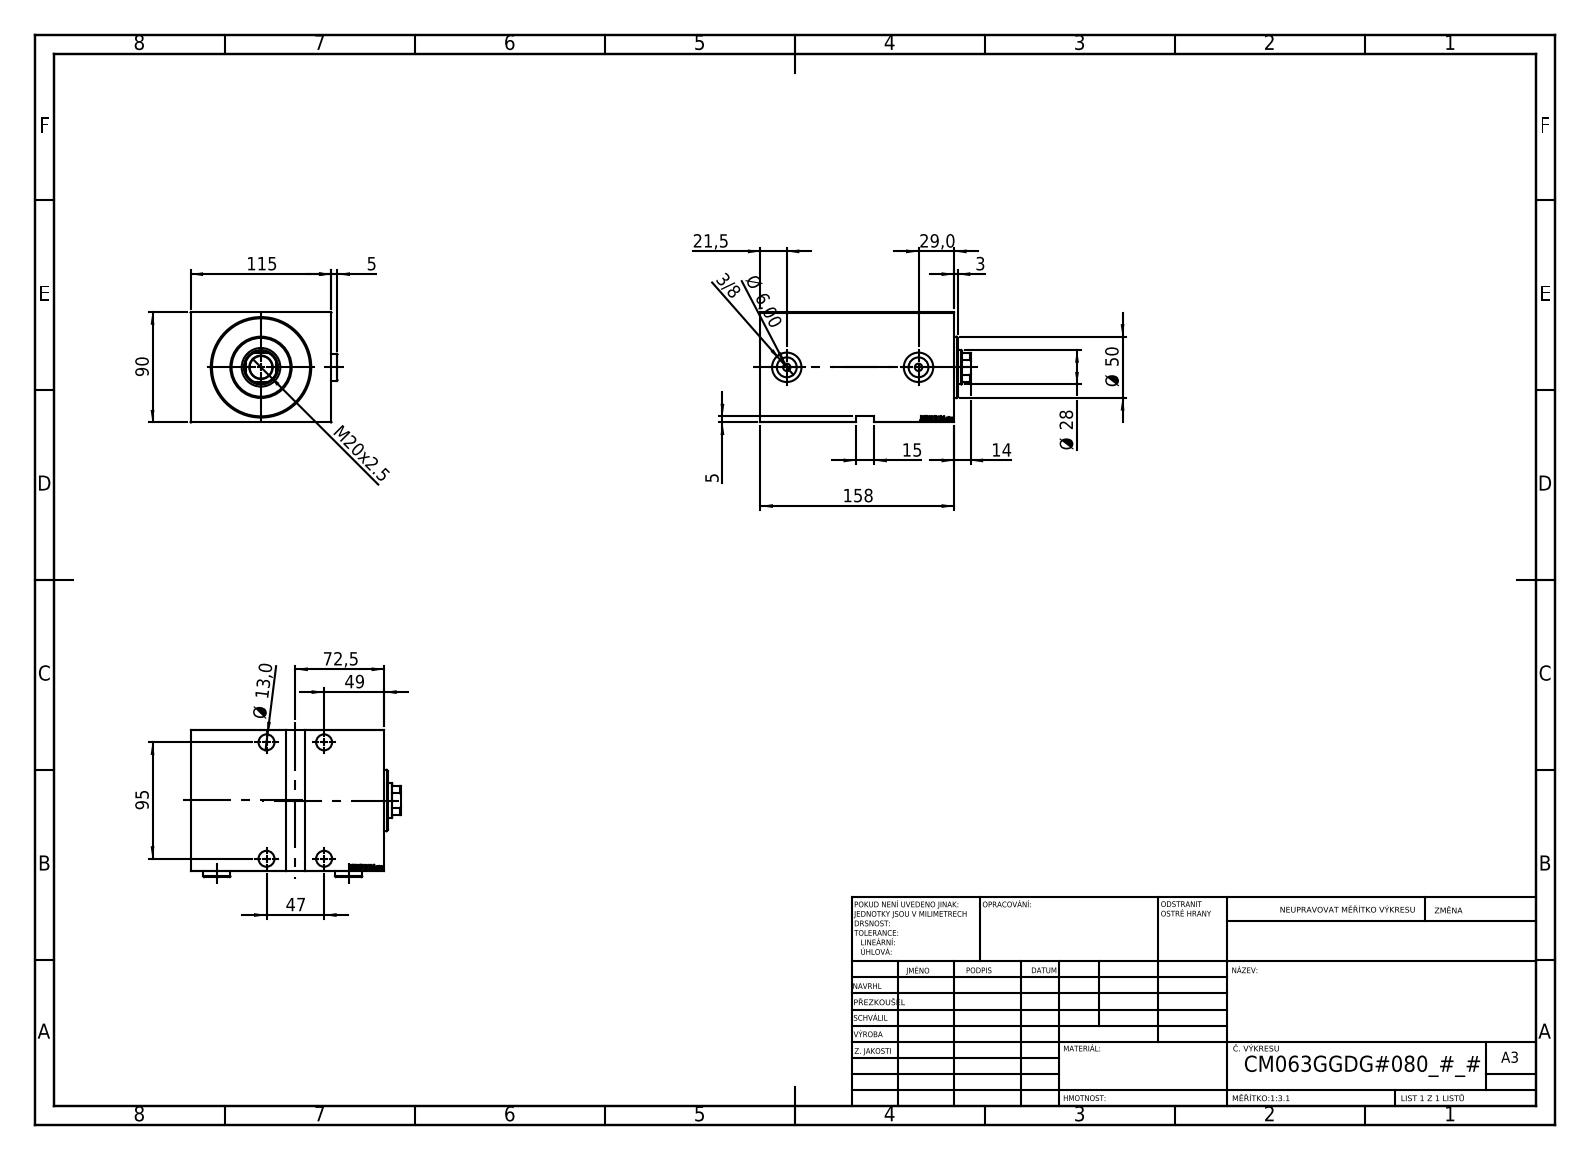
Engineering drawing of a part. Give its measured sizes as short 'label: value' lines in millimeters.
name: V450CM_VC_G; V450CM_G_VCP; Zatka_OIL_PORT; V450CM_G_Body
written by: SolidWorks 2019 (CONFIG_CONTROL_DESIGN)
unit: mm
bodies: 5 solids, 912 faces (446 planar, 68 cylindrical, 398 other)
size: 171.5 × 119.9 × 90
volume: 1 337 000 mm³; area: 173 139 mm²
holes: 4× ⌀13, 4× ⌀19, 2× ⌀6, 2× ⌀16.17, 2× ⌀24, 1× ⌀18.5, 1× ⌀28, 1× ⌀31.5, 1× ⌀63, 1× ⌀65, 1× ⌀80
bosses: 2× ⌀22, 1× ⌀50
rounds: 1× R13.5
face distances: 90, 115, 5, 158, 17.5, 140.5, 153, 135.5, 93.5, 64.5
hole spacings: 47, 95, 105.99, 107.5
